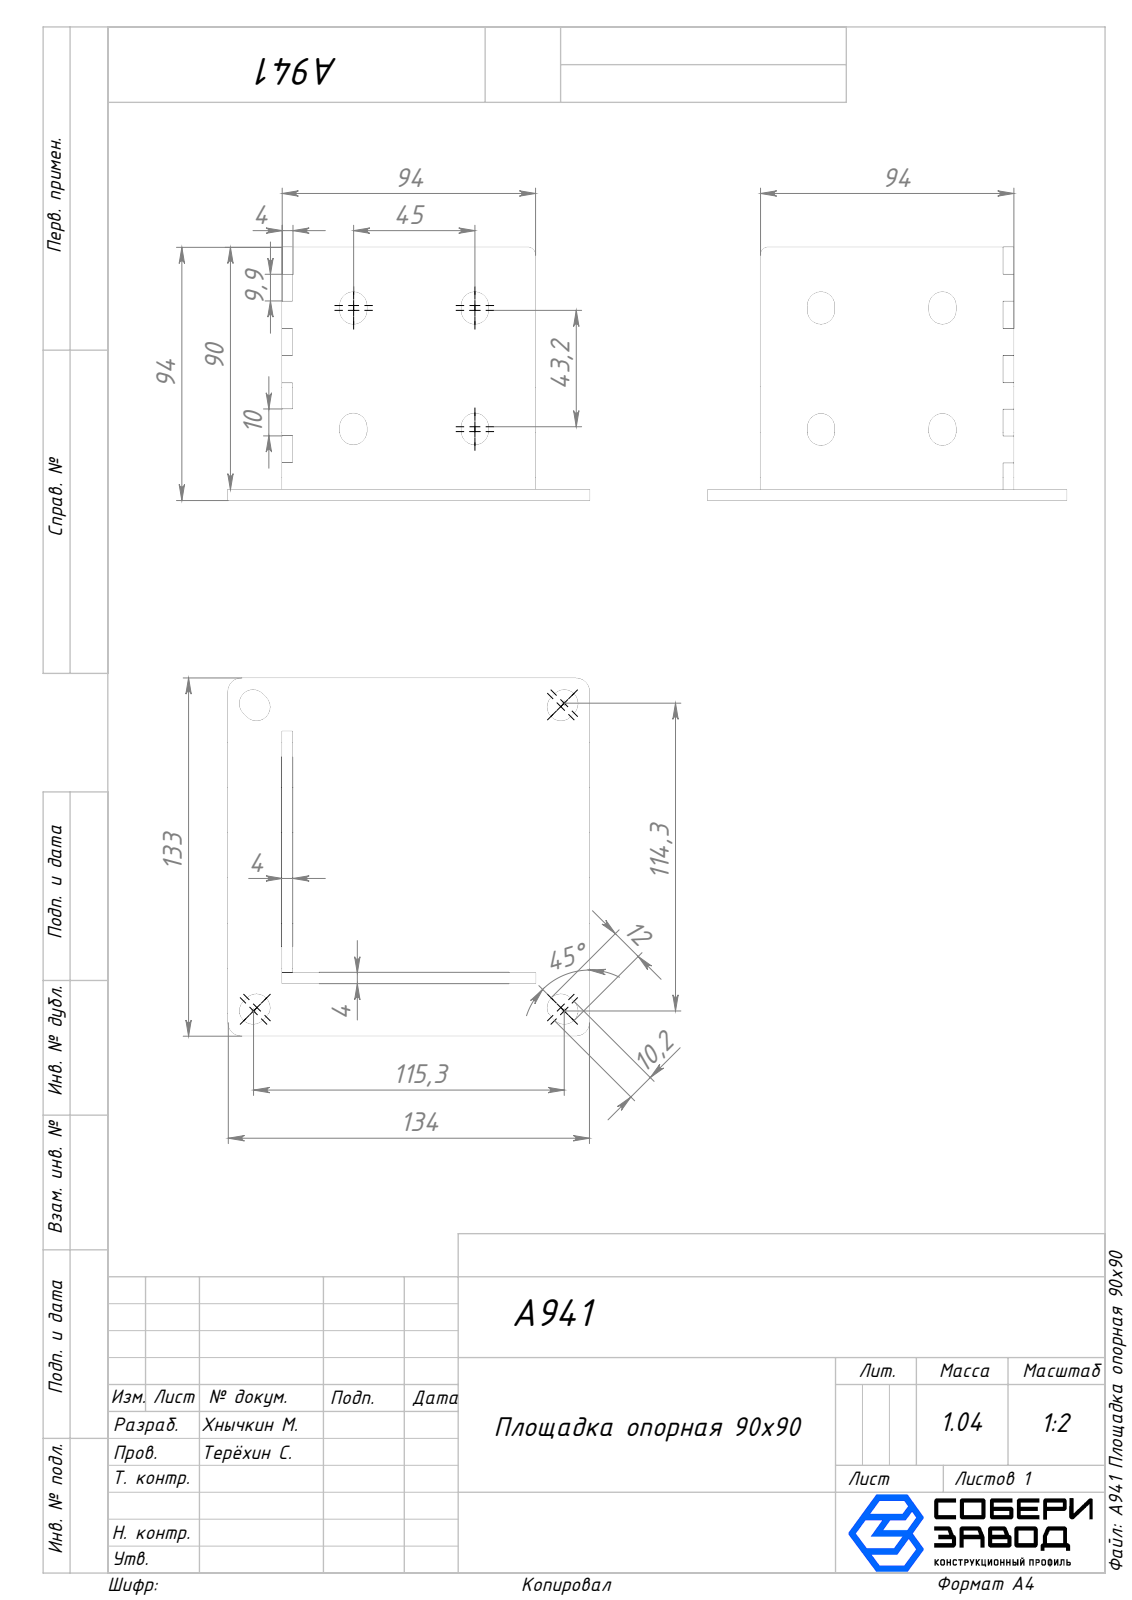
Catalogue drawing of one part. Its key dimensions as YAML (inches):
part_name: "A941 90x90 Основание_00; A941 90x90 Боковина с пазом 2_00; A941 Площадка опорная 90x90; A941 90x90 Боковина с пазом 1_00"
step_written_by: "SolidWorks 2025 (AUTOMOTIVE_DESIGN)"
units: inches
bodies: {solids: 3, faces: 128, planar: 90, cylindrical: 38, other: 0}
overall_size: [5.276, 5.236, 3.701]
volume: 8.077
surface_area: 115.3
partial_cylinders:
  - {radius: 0.201, count: 24}
  - {radius: 0.197, count: 4}
  - {radius: 0.118, count: 2}
face_to_face_distances: [0.157, 3.701, 3.543, 0.165, 0.787, 0.768, 4.469, 4.488, 3.709, 0.173]
